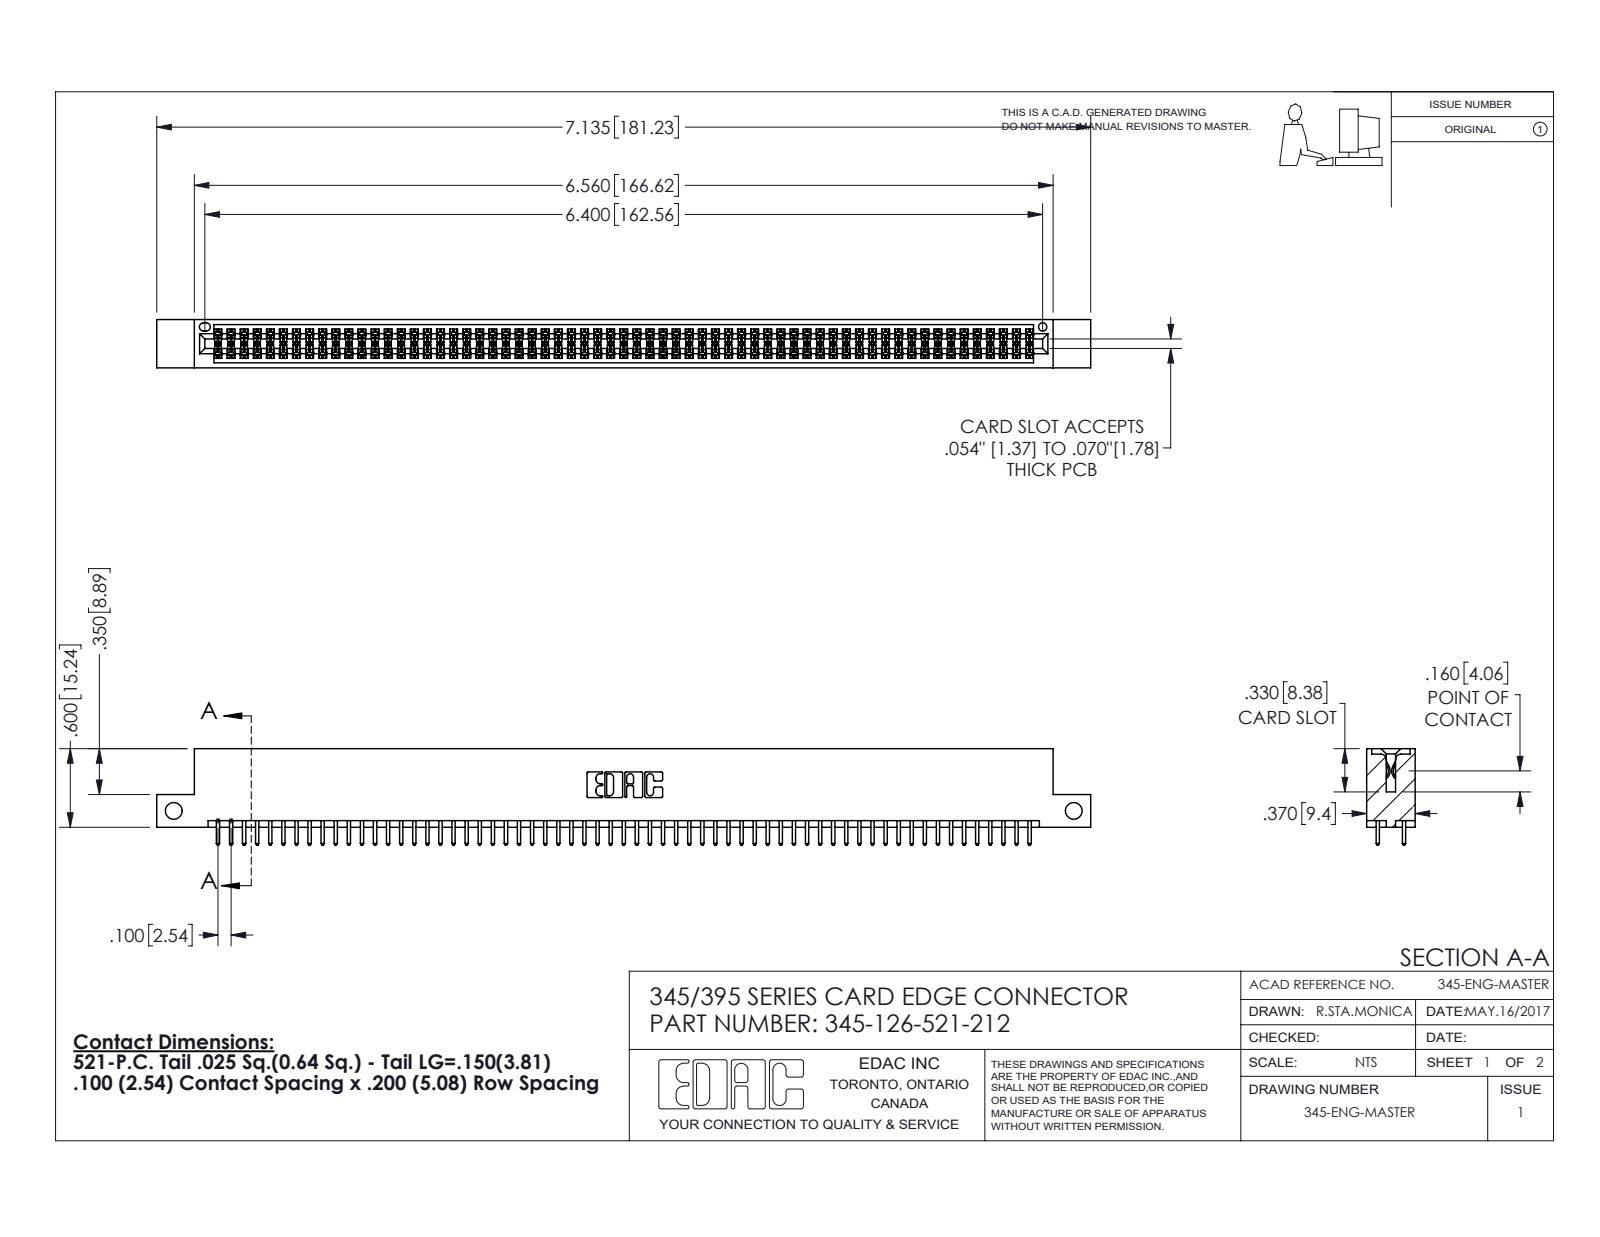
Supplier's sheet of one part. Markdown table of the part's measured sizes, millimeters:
| quantity | value |
| --- | --- |
| part name | 345-126-521-212; 345-292-001_345-293-121; 345 Part_Flush Mounting Lugs - Side Mount |
| STEP written by | SolidWorks 2016 (CONFIG_CONTROL_DESIGN) |
| units | millimeters |
| bodies | 127 solids, 6426 faces (4238 planar, 2188 cylindrical, 0 other) |
| overall size | 181.2 × 18.7 × 9.4 |
| volume | 17 670 mm³ |
| surface area | 26 050 mm² |
| round holes (diameter × count) | 3.3 × 2, 1.6 × 1 |
| partial cylindrical surfaces (radius × count) | 0.2 × 189, 0.3 × 126, 0.3 × 22, 0.2 × 6, 0.8 × 6, 0.7 × 3, 0.4 × 2, 0.5 × 2 |
| main face-to-face distances | 7.6, 1.8, 5.1, 2.5, 6.9, 0.6, 9.4, 5.7, 4.4, 3.8 |
| hole center spacings | 174.6 |
